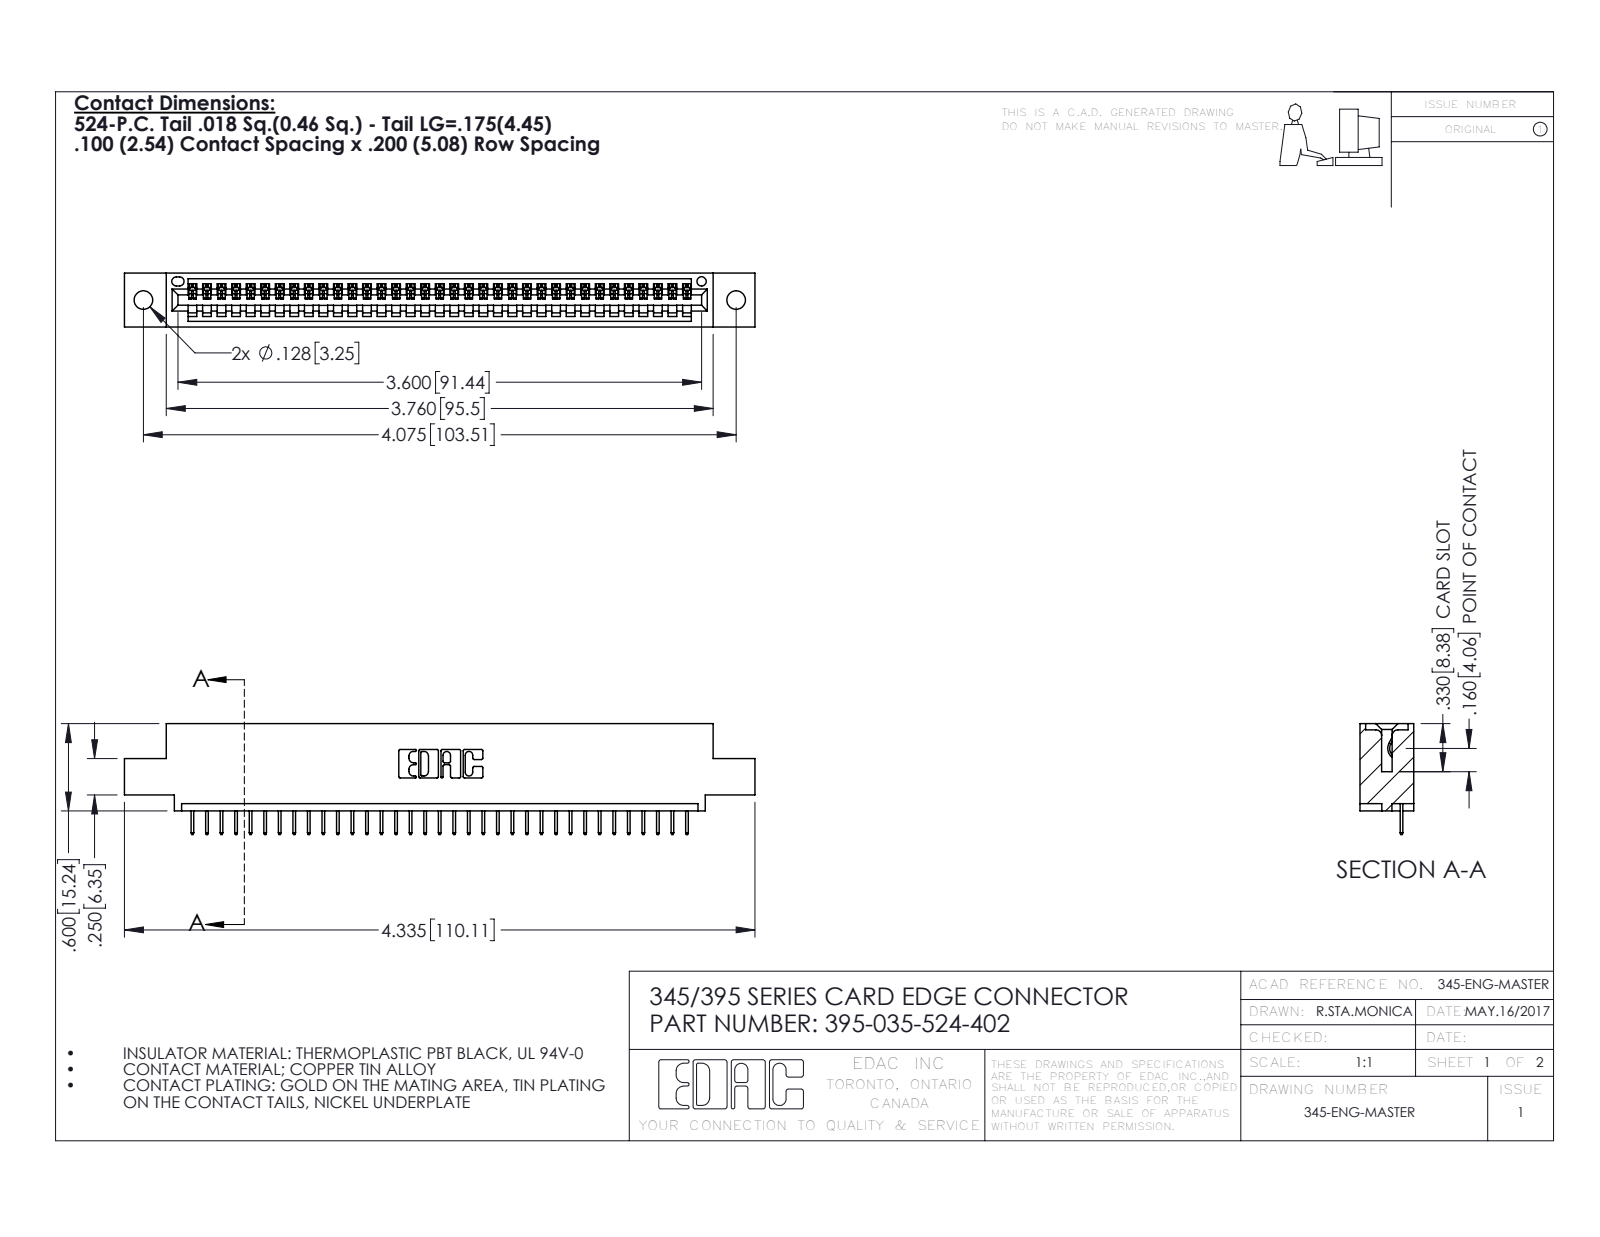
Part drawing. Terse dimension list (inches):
name: 395-035-524-402; 345 Part_0.110 Offset - 0.128 Dia; 345-292-001_345-293-124
written by: SolidWorks 2016 (CONFIG_CONTROL_DESIGN)
unit: in
bodies: 36 solids, 2300 faces (1694 planar, 606 cylindrical, 0 other)
size: 4.335 × 0.762 × 0.37
volume: 0.62 in³; area: 19.79 in²
holes: 2× ⌀0.128, 1× ⌀0.064
rounds: 70× R0.006, 22× R0.01, 6× R0.007, 6× R0.031, 3× R0.026, 2× R0.031, 2× R0.04, 1× R0.014
face distances: 0.072, 0.298, 0.37, 0.2, 0.098, 0.272, 0.025, 0.225, 0.072, 0.149
hole spacings: 0.27, 3.839, 4.075
